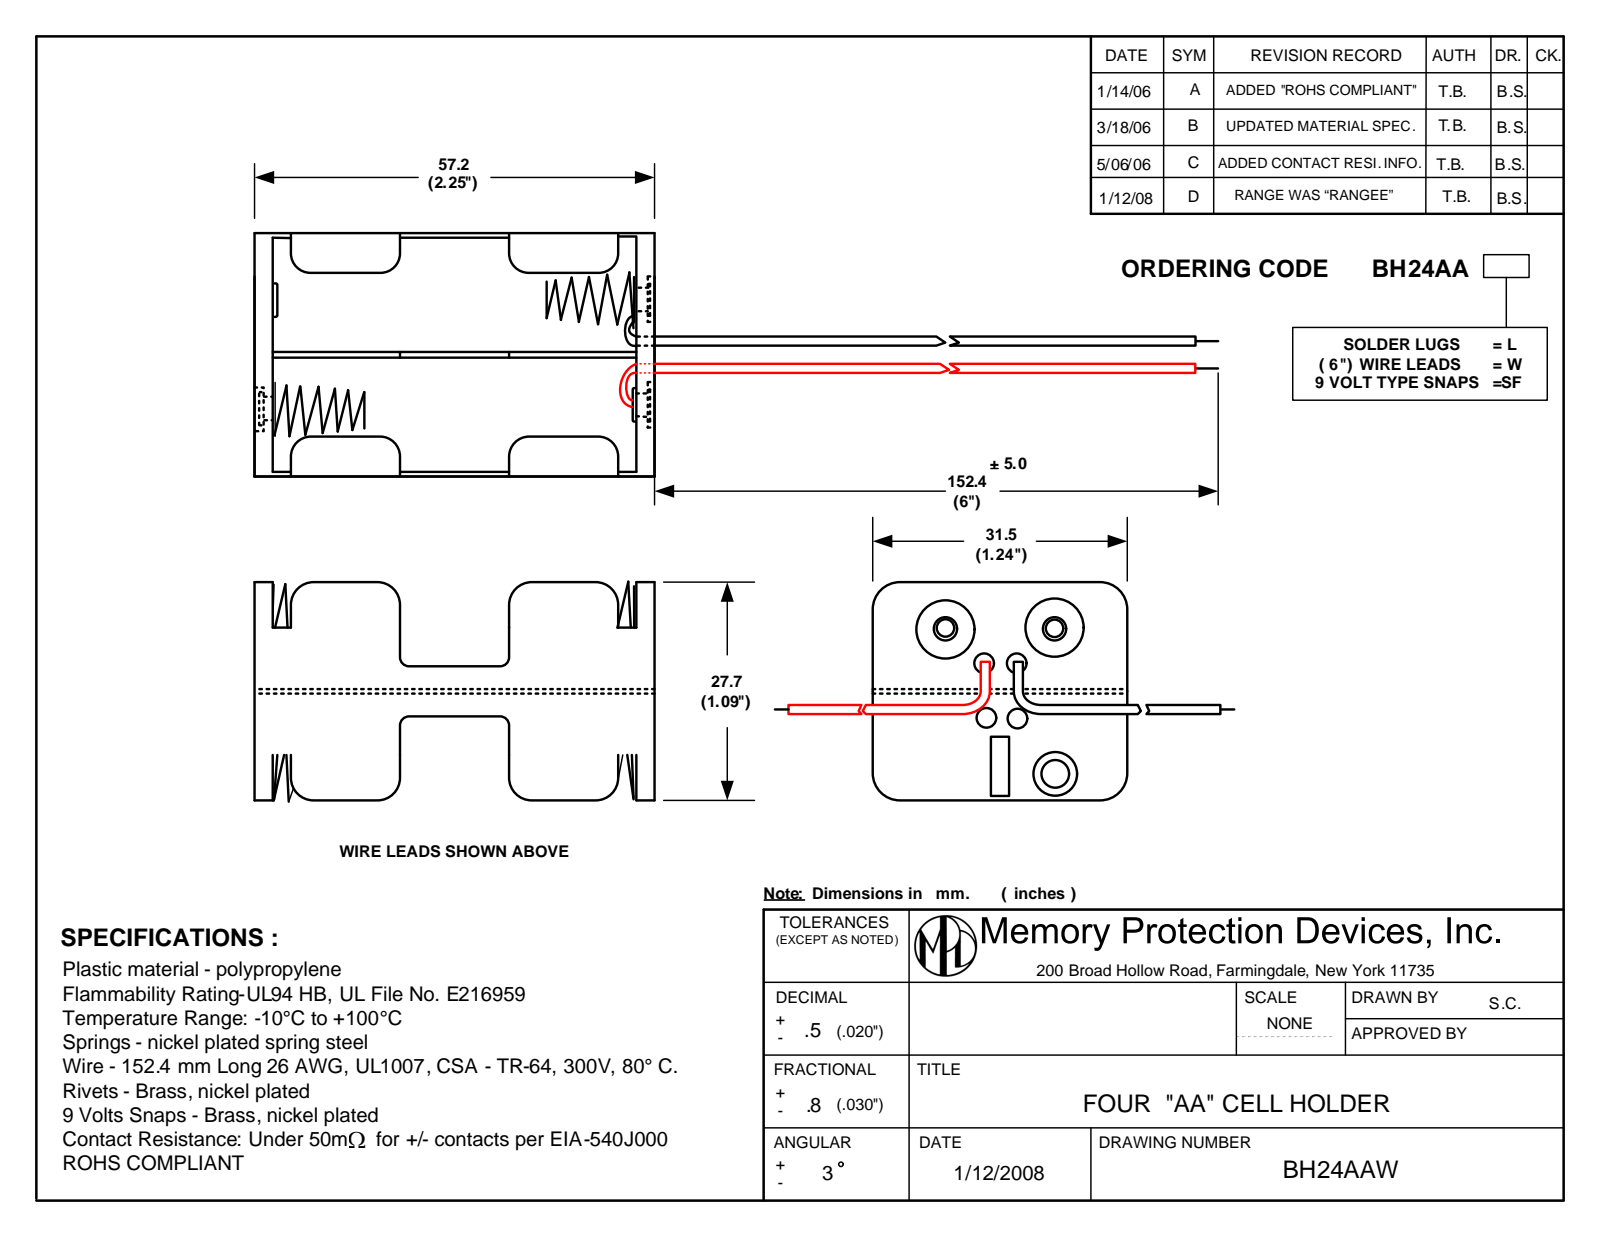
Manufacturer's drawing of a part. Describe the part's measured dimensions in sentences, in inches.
The part is named "BH24AAW". Its 3-D file was written by "SolidWorks 2017 (AUTOMOTIVE_DESIGN)". It is 13 solids with 644 faces: 236 planar, 256 cylindrical and 152 other. Overall it measures 8.346 by 1.235 by 1.08 inches. Its volume is 0.635 cubic inches and its surface area 24.1 square inches. Round holes: 6 of diameter 0.146, 4 of diameter 0.087, 4 of diameter 0.091, 4 of diameter 0.118, 4 of diameter 0.299, 2 of diameter 0.016, 2 of diameter 0.063. Round bosses or shafts: 6 of diameter 0.185, 4 of diameter 0.244, 4 of diameter 0.024, 2 of diameter 0.138, 2 of diameter 0.032. Partial cylindrical surfaces (rounded edges, fillets, slot ends): 22 of radius 0.008, 16 of radius 0.098, 4 of radius 0.118, 4 of radius 0.161, 4 of radius 0.165. The main face-to-face distances are 0.043, 0.122, 2.201, 0.596, 0.596, 1.192, 1.235, 2.157, 2.244, 0.639. The hole center spacings are 1.496, 0.28, 0.379, 0.458, 0.524, 1.619, 0.13, 0.209.
